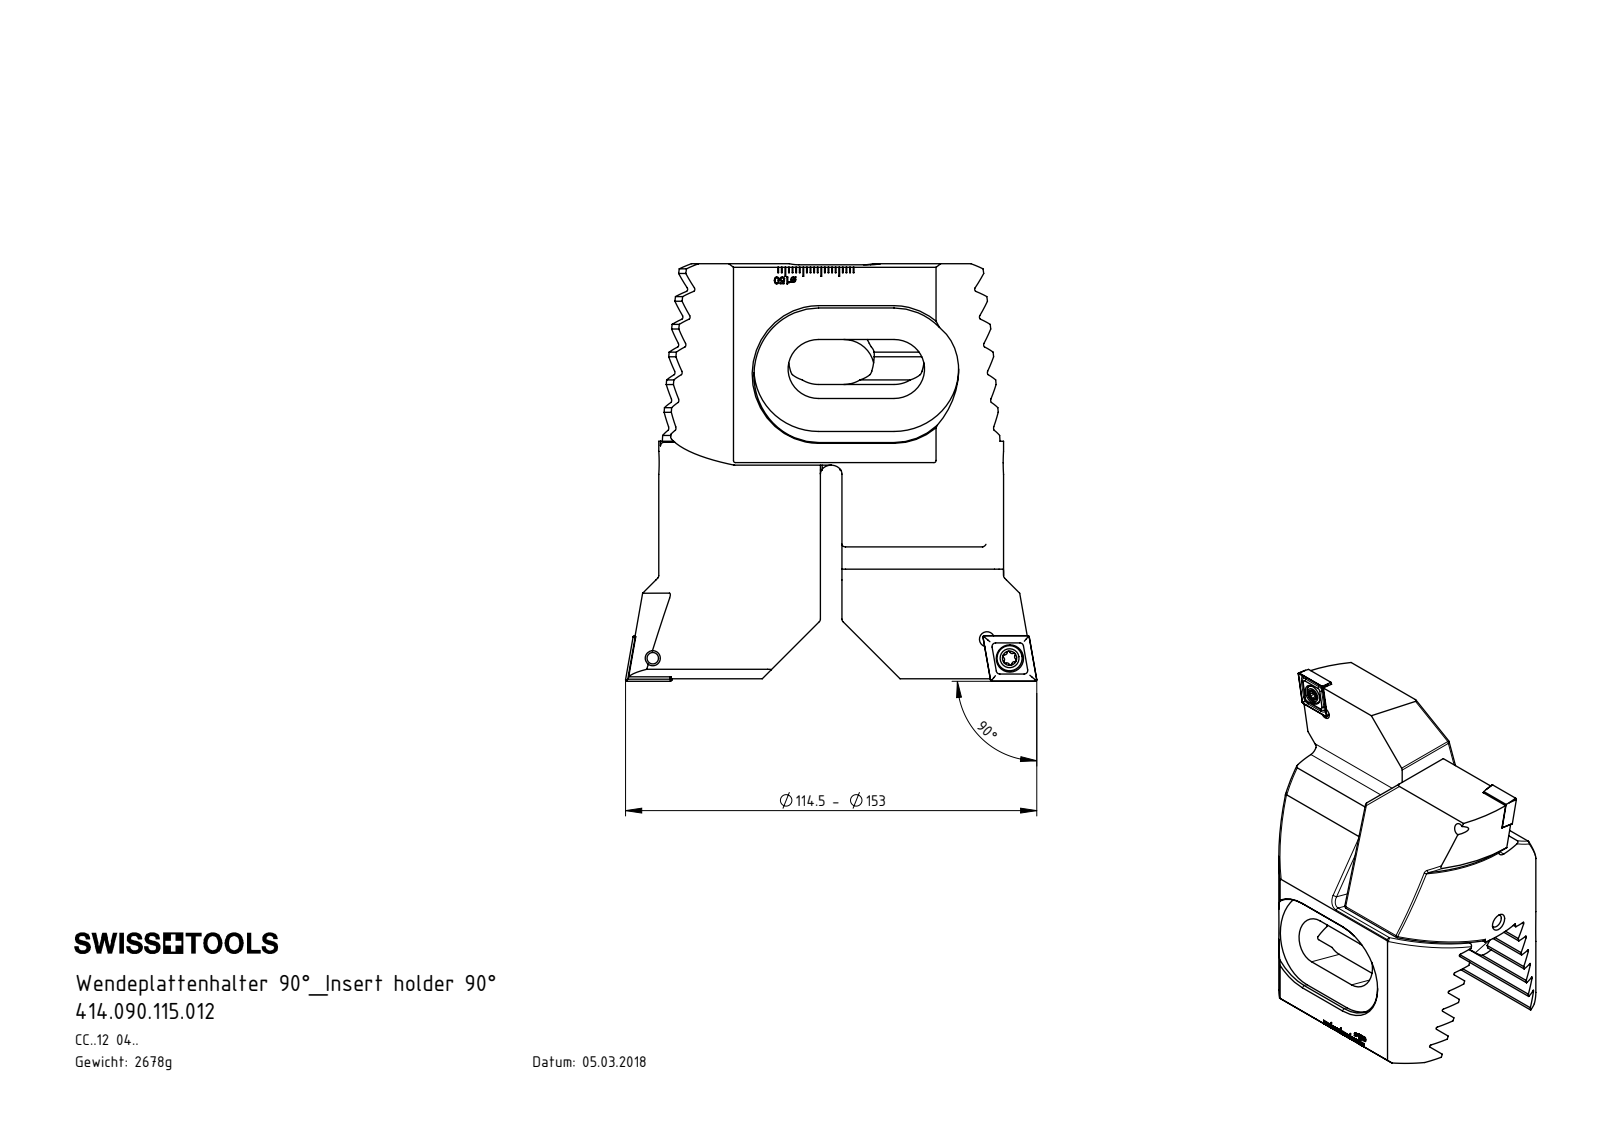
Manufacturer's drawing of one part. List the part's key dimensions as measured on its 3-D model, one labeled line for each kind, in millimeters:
Part name (STEP PRODUCT): 414.090.115.012; WCC-ER2.001.010_A; CCMT120404; Z94-ER3.001.040 (+1 more)
STEP written by: SolidWorks 2017 (CONFIG_CONTROL_DESIGN)
Units: millimetres
Bodies: 8 solids, 788 faces (448 planar, 136 cylindrical, 204 other)
Overall size (bounding box): 115.5 × 114.5 × 75.2
Volume: 343 054 mm³ · Surface area: 64 566 mm²
Round holes (diameter × count): ⌀4.2 ×4, ⌀2 ×2, ⌀5.5 ×2, ⌀7.6 ×2, ⌀5 ×1
Round bosses / shafts (diameter × count): ⌀7 ×2, ⌀5 ×2, ⌀6 ×1, ⌀4 ×1
Partial cylindrical surfaces — rounded edges, fillets, slot ends (radius × count): R1 ×16, R0.39 ×12, R0.58 ×12, R0.69 ×8, R3 ×6, R0.69 ×4, R8.5 ×4, R12 ×4
Main face-to-face distances: 6.93, 20.78, 27.71, 13.85, 13.86, 13.19, 37.3, 37.9, 6.92, 6
Hole centre spacings: 8.21, 8.33, 25, 93.2, 93.29, 99.43, 48.3, 86.76
